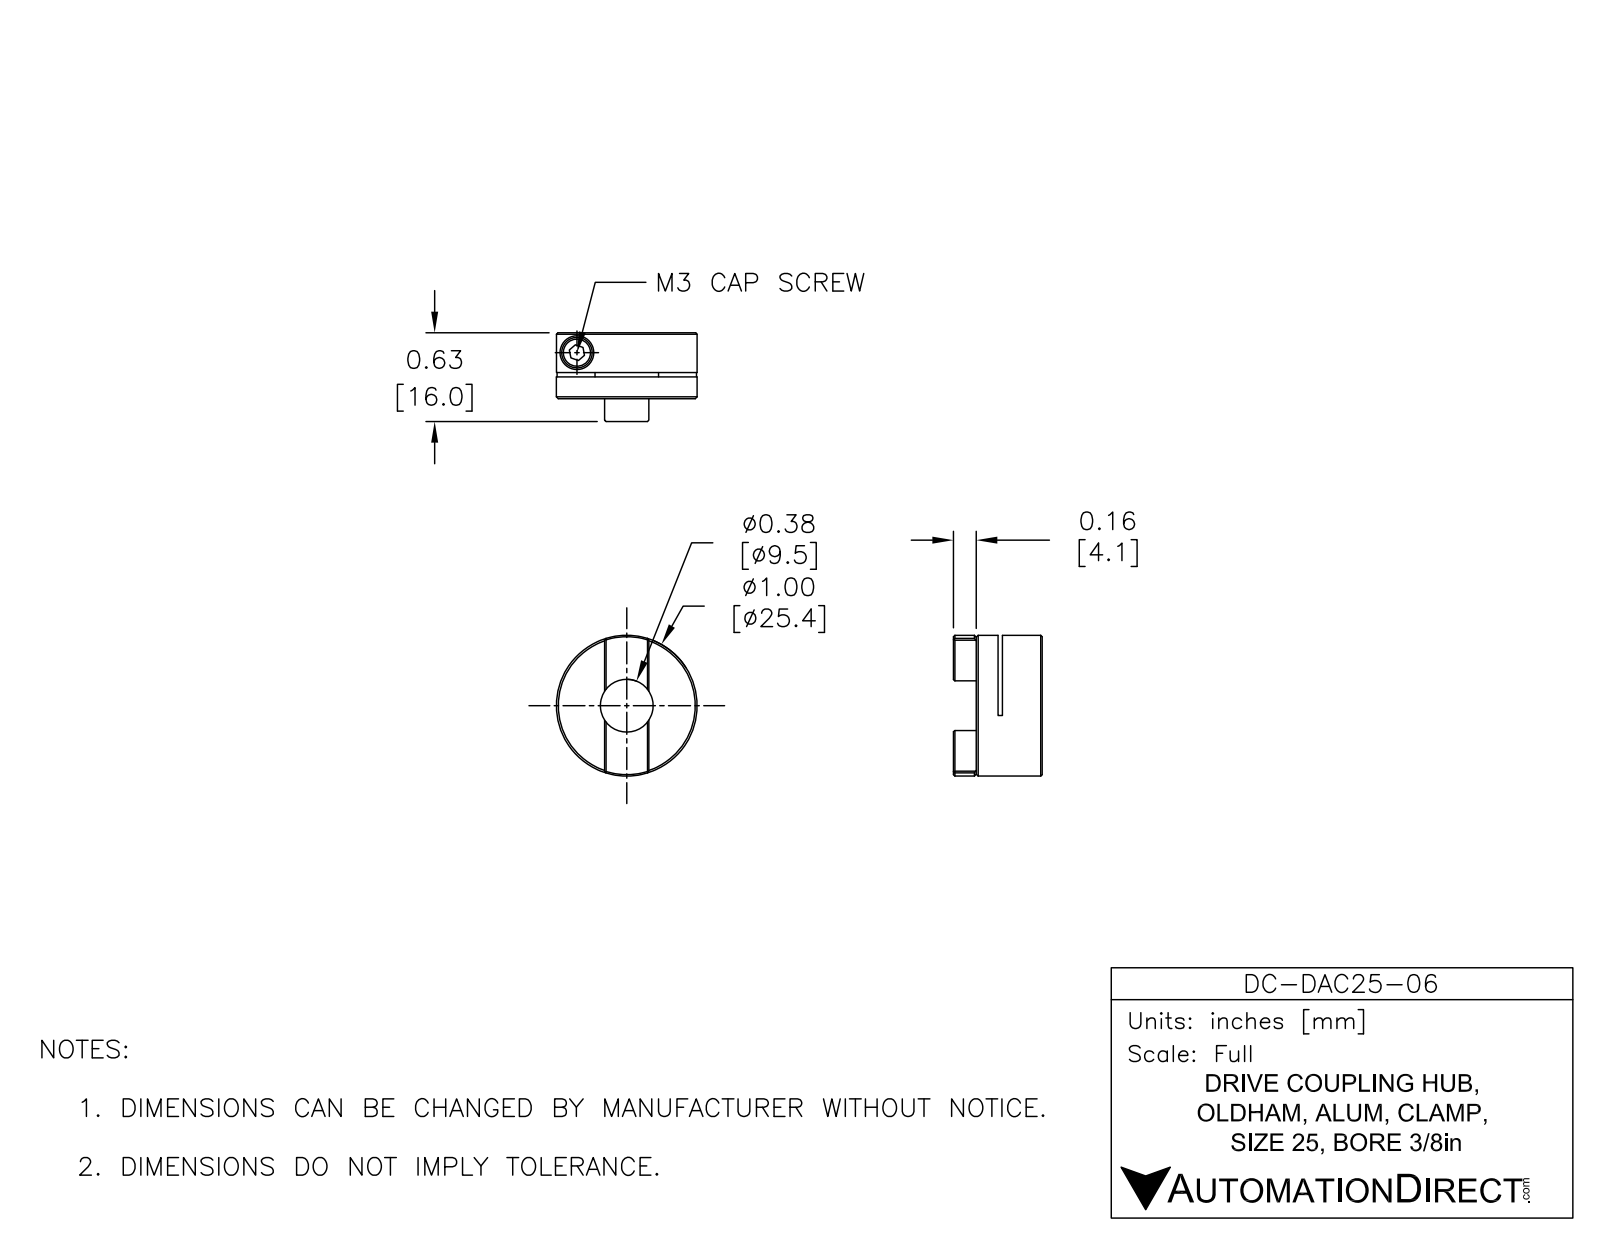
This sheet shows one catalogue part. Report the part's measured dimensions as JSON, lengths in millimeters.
{"part_name": "DC-DAC25-06", "step_written_by": "SolidWorks 2015 (AUTOMOTIVE_DESIGN)", "units": "millimeters", "bodies": {"solids": 1, "faces": 55, "planar": 29, "cylindrical": 16, "other": 10}, "overall_size": [25.4, 25.4, 15.66], "volume_mm3": 5135, "surface_area_mm2": 3141, "round_holes": [[2.46, 1], [3.4, 1], [6.1, 1], [9.53, 1]], "round_bosses_or_shafts": [[25.4, 1]], "partial_cylinders_radius": [[25.4, 1]], "face_to_face_distances": [11.89, 7.95, 3.94, 7.16, 0.79, 4.73, 15.66, 8.5, 7.71, 3.77]}
